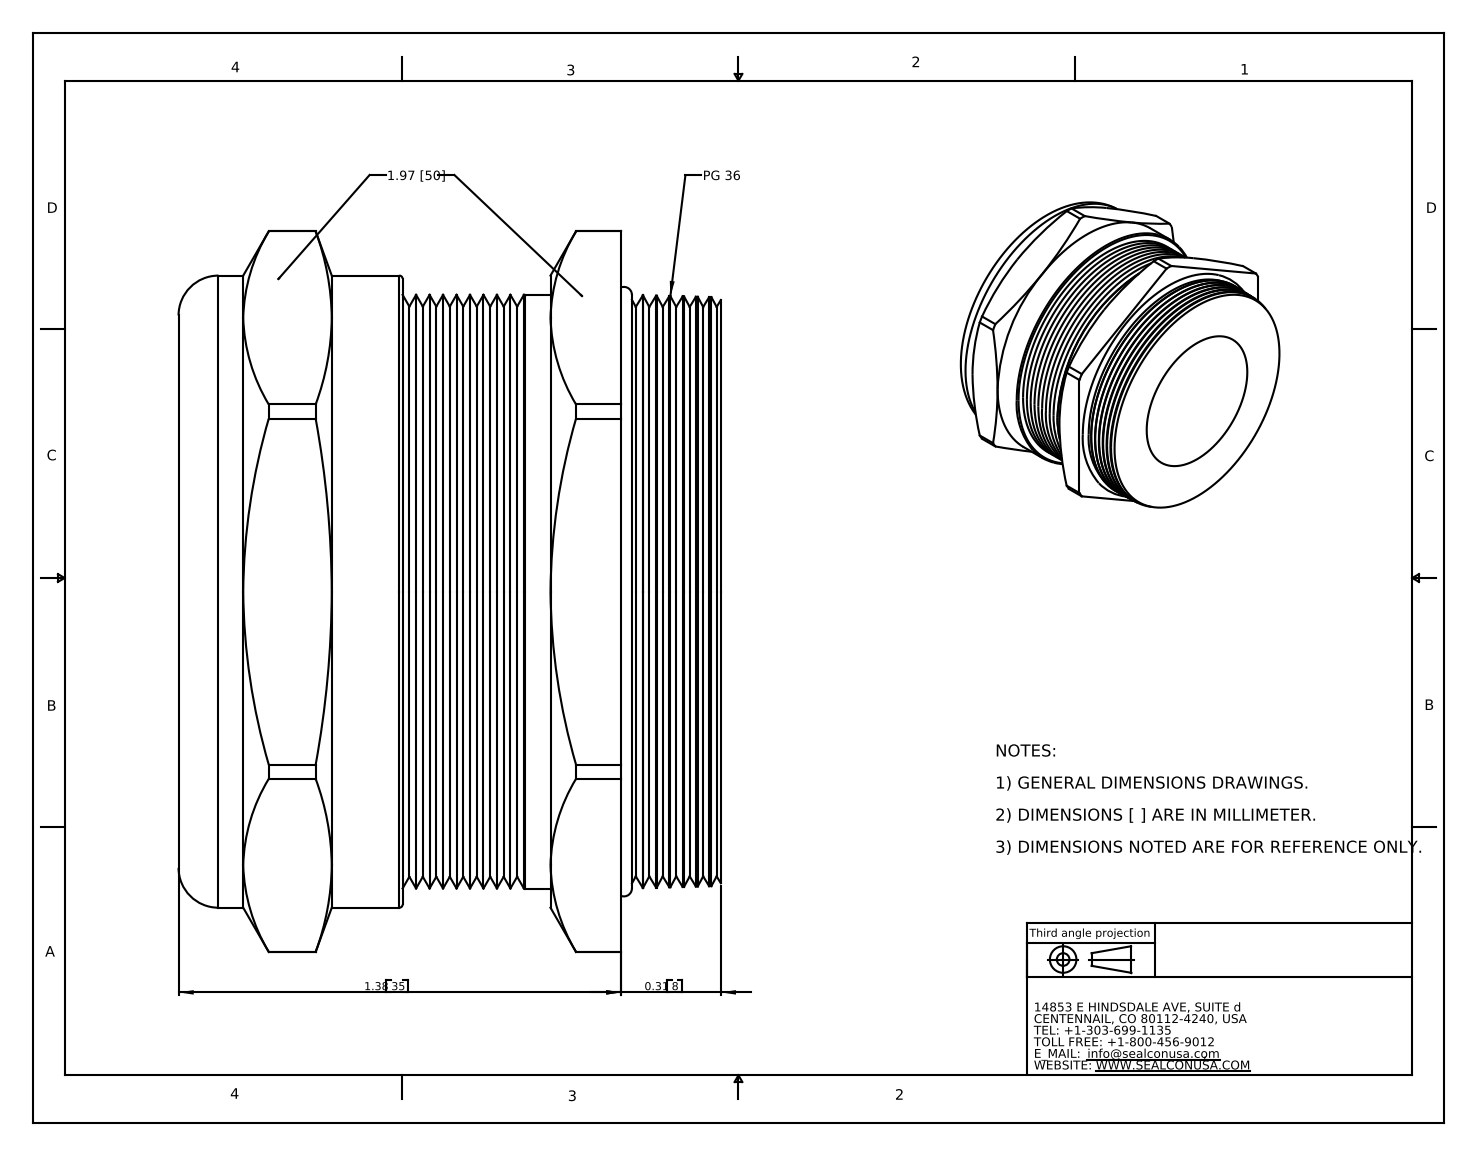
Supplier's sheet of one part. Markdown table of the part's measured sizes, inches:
| quantity | value |
| --- | --- |
| part name | CD36AR-SS |
| STEP written by | SolidWorks 2007 (CONFIG_CONTROL_DESIGN) |
| units | inches |
| bodies | 2 solids, 158 faces (22 planar, 28 cylindrical, 108 other) |
| overall size | 2.246 × 1.97 × 1.69 |
| volume | 3.461 in³ |
| surface area | 28.25 in² |
| round holes (diameter × count) | 1.02 × 1, 1.428 × 1, 1.85 × 1 |
| round bosses / shafts (diameter × count) | 1.97 × 1, 1.852 × 1 |
| partial cylindrical surfaces (radius × count) | 1.123 × 1 |
| main face-to-face distances | 1.488, 1.97, 0.181, 1.67, 0.02, 0.202, 1.69, 1.38, 1.36, 1.178 |
